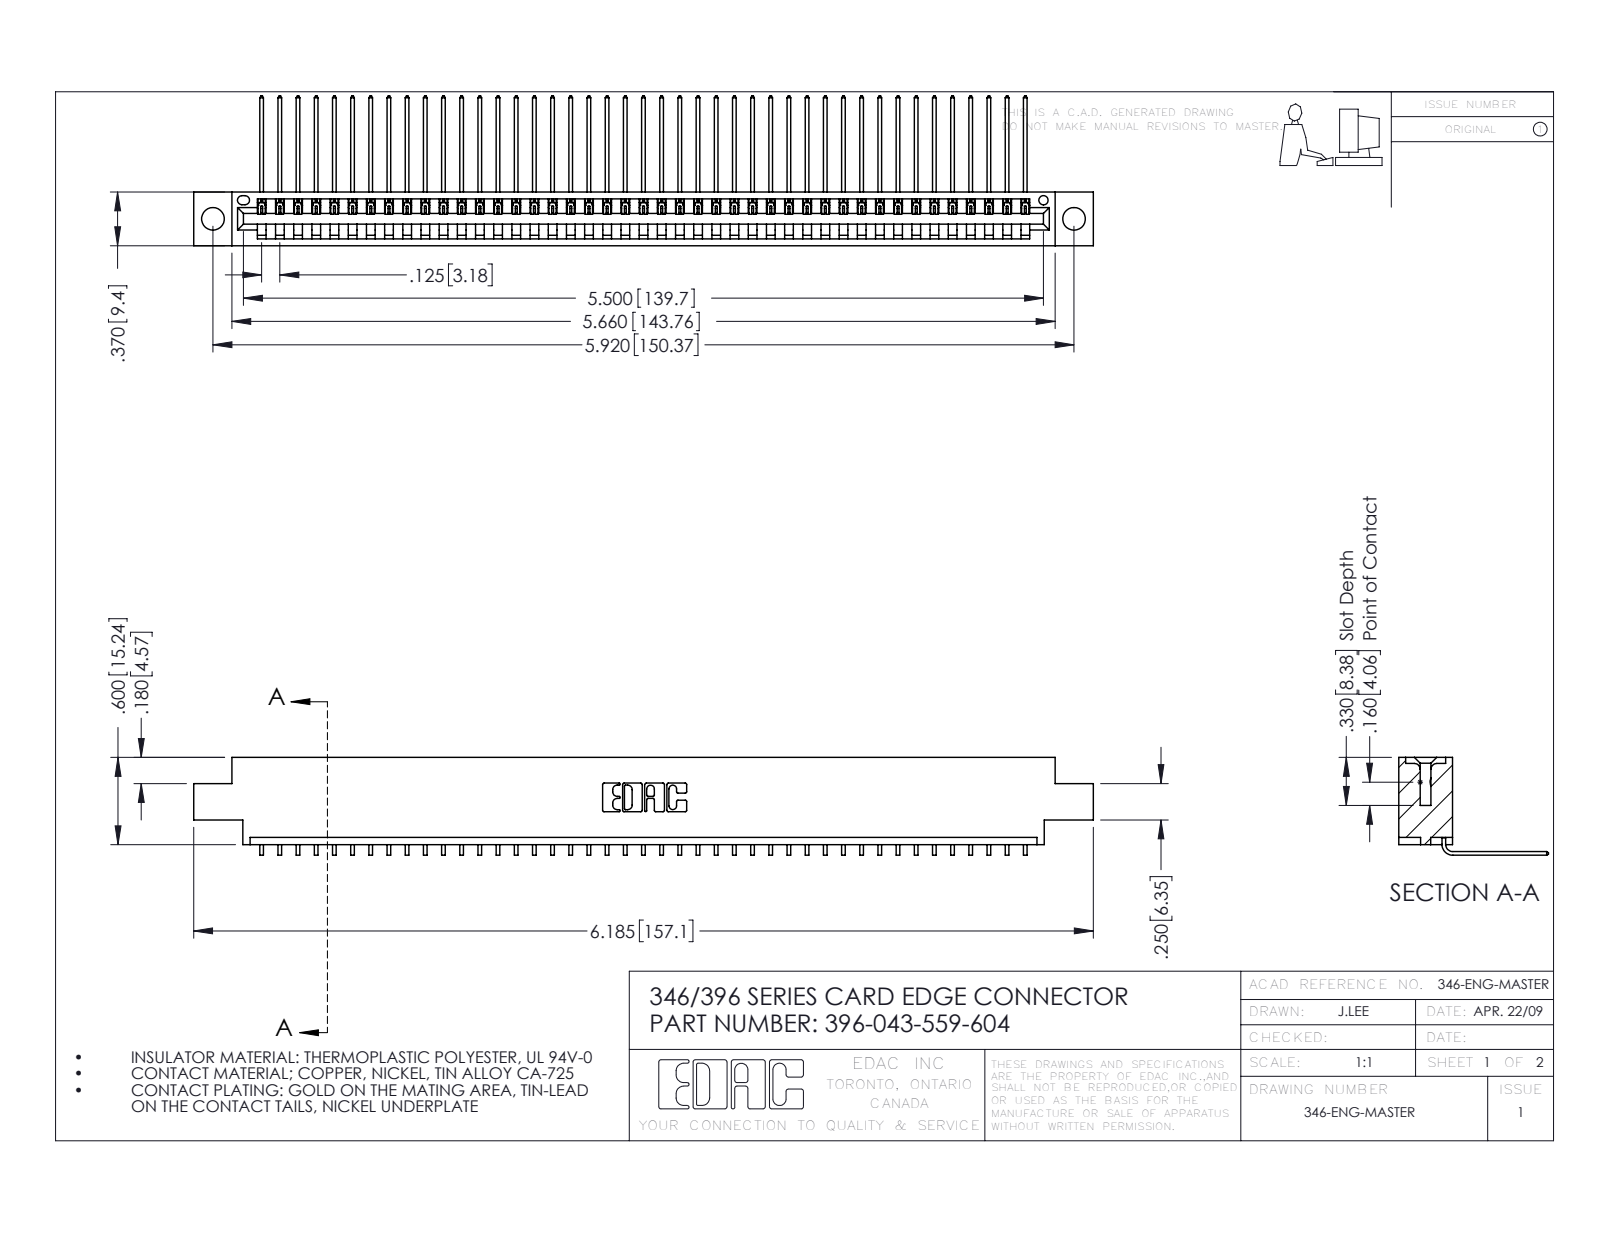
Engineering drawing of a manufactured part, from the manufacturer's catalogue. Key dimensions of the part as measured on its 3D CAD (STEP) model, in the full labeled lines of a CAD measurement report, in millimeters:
Part name (STEP PRODUCT): 396-043-559-604; 345-292-001_558 559 Tail - 1; 346 Part_0.170 Offset - 0.156 Dia-TH
STEP written by: SolidWorks 2016 (CONFIG_CONTROL_DESIGN)
Units: millimetres
Bodies: 44 solids, 2706 faces (1886 planar, 820 cylindrical, 0 other)
Overall size (bounding box): 157.1 × 26.2 × 17.1
Volume: 14 900 mm³ · Surface area: 19 510 mm²
Round holes (diameter × count): ⌀4 ×2, ⌀1.6 ×1
Partial cylindrical surfaces — rounded edges, fillets, slot ends (radius × count): R0.2 ×86, R0.3 ×22, R0.2 ×6, R0.8 ×6, R0.7 ×3, R0.8 ×2, R1 ×2, R0.4 ×1
Main face-to-face distances: 1.2, 8.2, 9.4, 0.6, 6.4, 1.8, 7.6, 3.8, 5.6, 2.5
Hole centre spacings: 6.2, 145.1, 150.4
